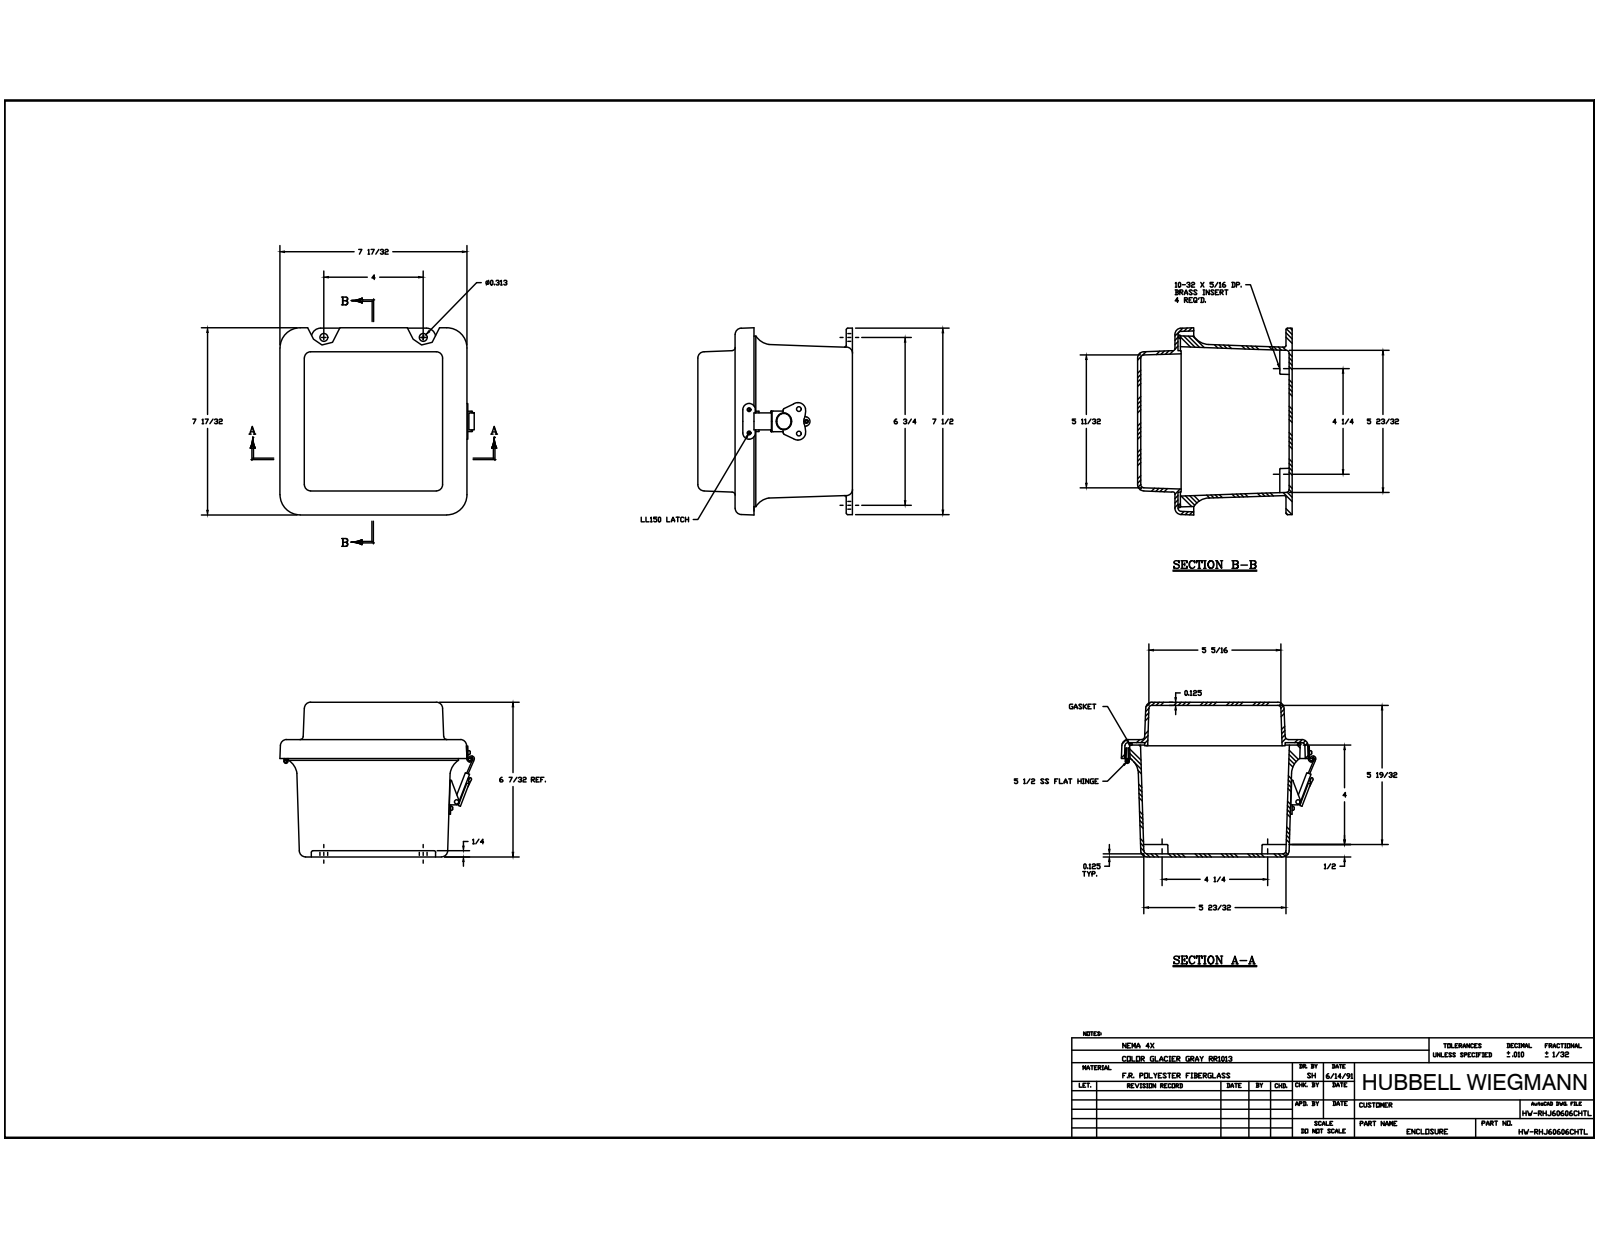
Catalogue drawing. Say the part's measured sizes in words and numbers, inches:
The part is named "J606HL_4; RMINS45821P_115; RMINS45821P_116; RMINS45821P_117 (+8 more)". Its 3-D file was written by "Autodesk Inventor 2014 (AUTOMOTIVE_DESIGN)". It is 30 solids with 781 faces: 317 planar, 294 cylindrical and 170 other. Overall it measures 7.629 by 7.525 by 6.338 inches. Its volume is 40.56 cubic inches and its surface area 579.3 square inches. Round holes: 9 of diameter 0.14, 5 of diameter 0.131, 5 of diameter 0.152, 4 of diameter 0.156, 4 of diameter 0.218, 2 of diameter 0.13, 2 of diameter 0.165, 2 of diameter 0.197, 1 of diameter 0.085, 1 of diameter 0.106, 1 of diameter 0.118, 1 of diameter 0.138. Round bosses or shafts: 9 of diameter 0.25, 9 of diameter 0.125, 4 of diameter 0.27, 1 of diameter 0.583, 1 of diameter 0.524, 1 of diameter 0.209, 1 of diameter 0.185, 1 of diameter 0.155. Partial cylindrical surfaces (rounded edges, fillets, slot ends): 20 of radius 0.031, 16 of radius 0.125, 16 of radius 0.25, 10 of radius 0.079, 4 of radius 0.037, 4 of radius 0.039, 4 of radius 0.045, 4 of radius 0.047. The main face-to-face distances are 0.125, 0.125, 1.5, 4.588, 6.088, 6.213, 6.338, 6.213, 4.713, 1.625. The hole center spacings are 5.308, 1.37, 2.5, 4.25, 6.187, 7.38, 0.469, 0.5.
